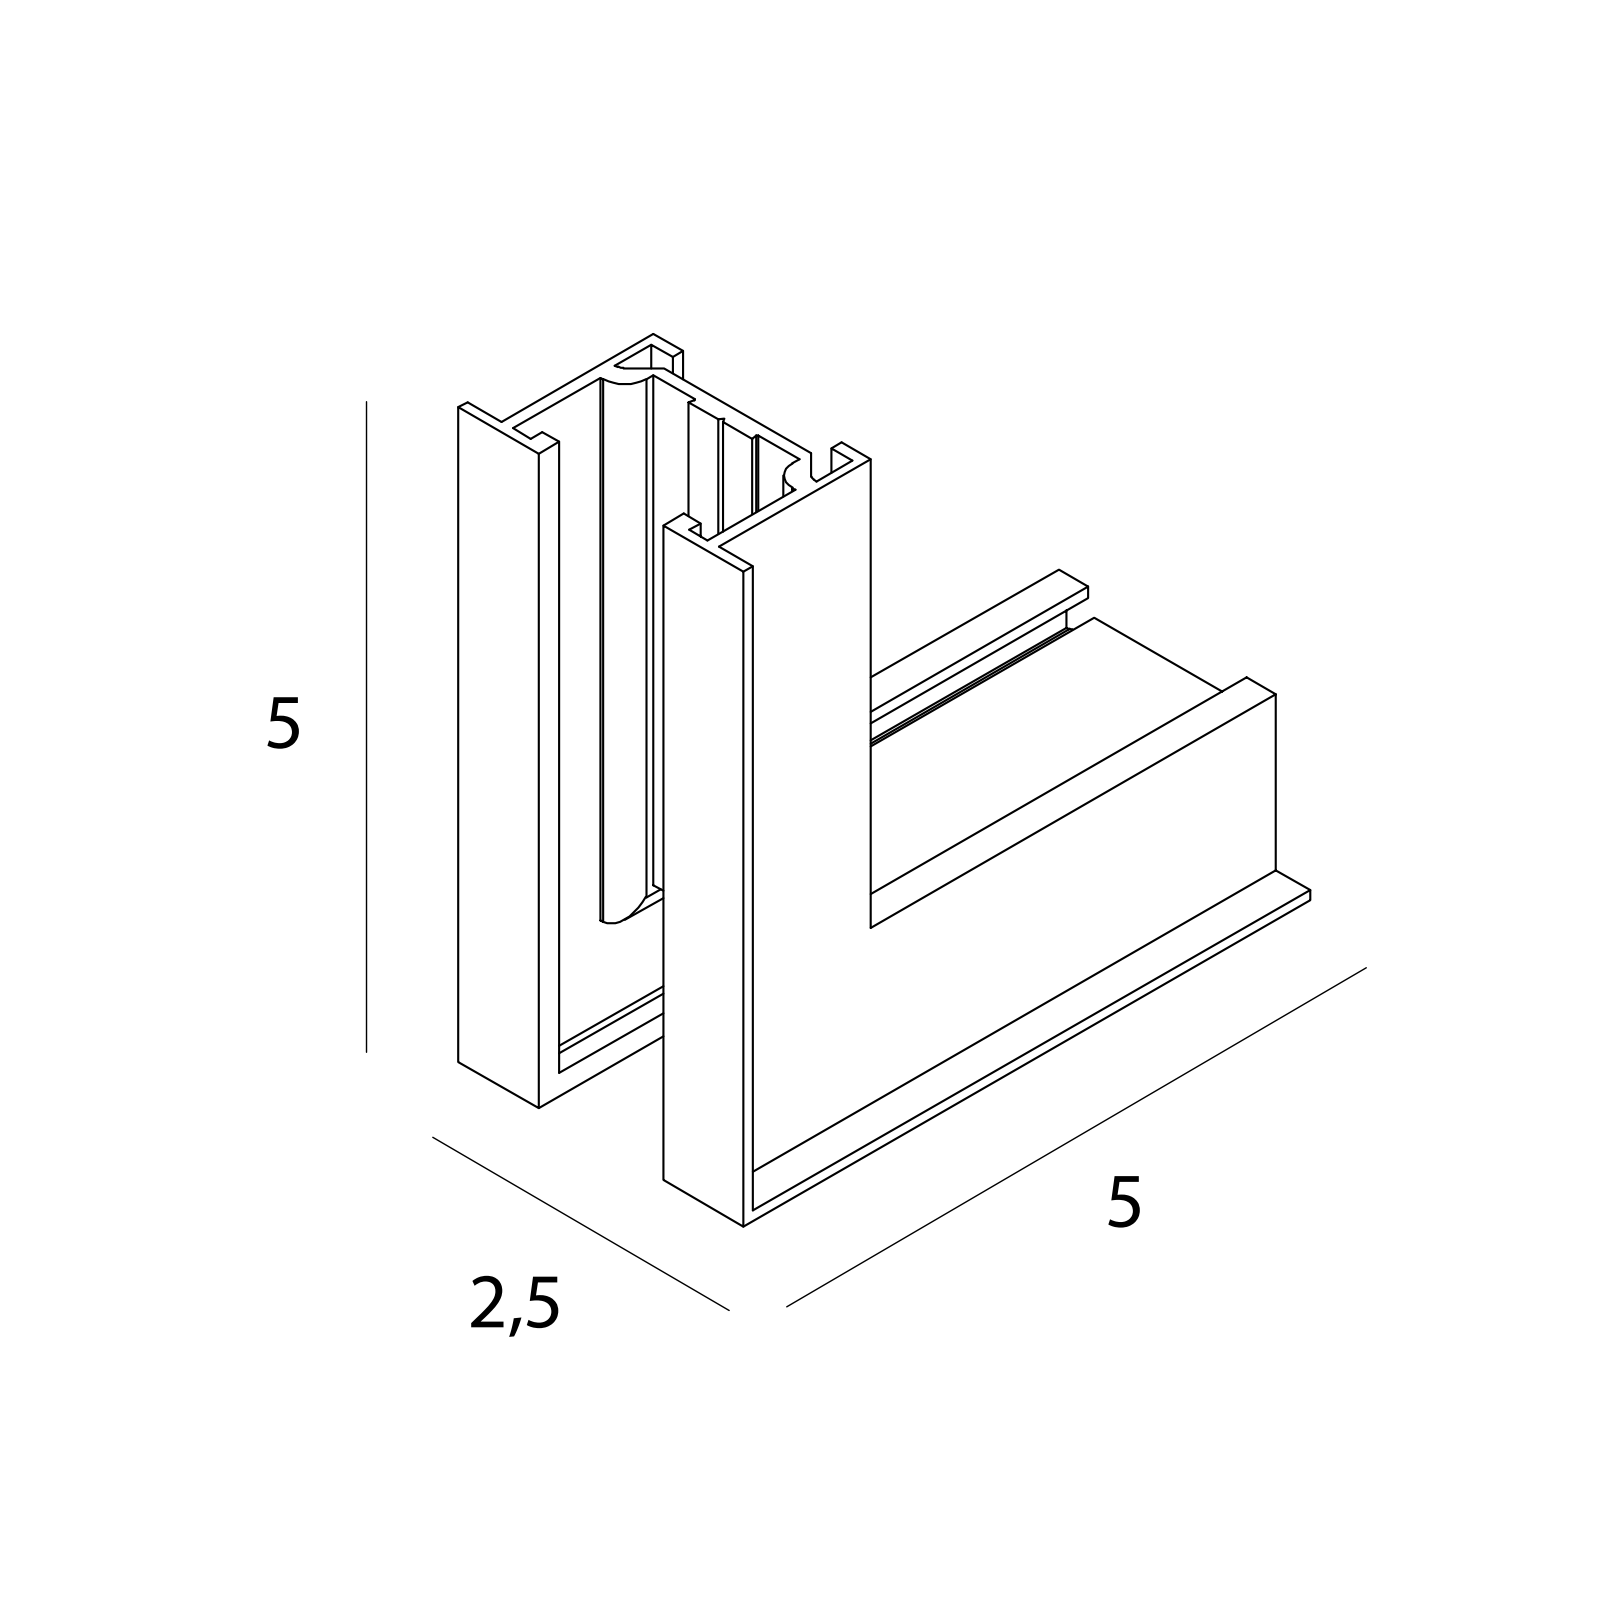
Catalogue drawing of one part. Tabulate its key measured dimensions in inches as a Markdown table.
| quantity | value |
| --- | --- |
| part name | NT0015 v3 |
| STEP written by | Autodesk Translation Framework v14.24.0.0 (AUTOMOTIVE_DESIGN) |
| units | inches |
| bodies | 1 solid, 84 faces (72 planar, 12 cylindrical, 0 other) |
| overall size | 1.969 × 1.969 × 0.991 |
| volume | 0.348 in³ |
| surface area | 18.05 in² |
| partial cylindrical surfaces (radius × count) | 0.004 × 4, 0.02 × 4, 0.075 × 4 |
| main face-to-face distances | 0.039, 0.716, 0.755, 0.475, 0.031, 0.444, 0.404, 0.676, 0.436, 0.028 |
